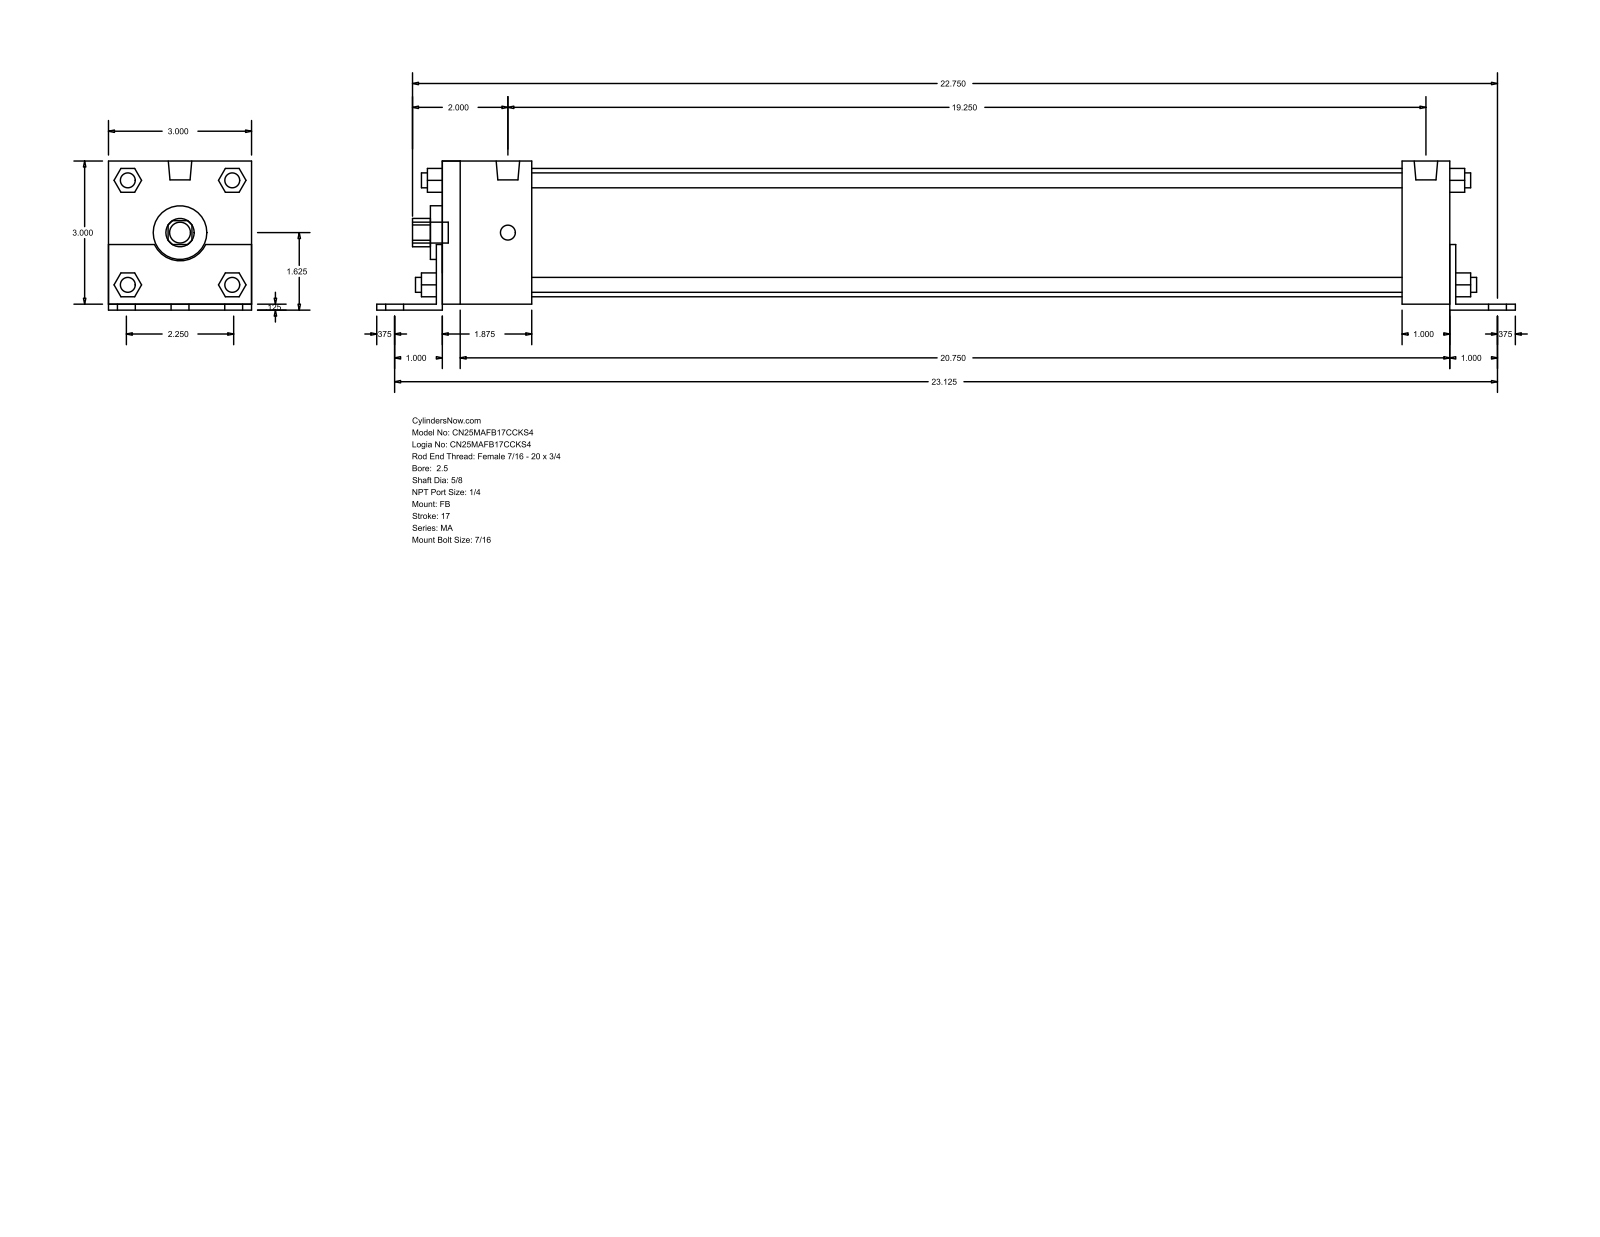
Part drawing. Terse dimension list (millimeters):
name: MA_FB__0250_0.625
written by: GSSL Pune (CONFIG_CONTROL_DESIGN)
unit: mm
bodies: 0 solids, 140 faces (105 planar, 35 cylindrical, 0 other)
size: 606.42 × 79.38 × 76.2
holes: 1× ⌀15.88, 1× ⌀28.57, 1× ⌀68.33
bosses: 8× ⌀7.94, 7× ⌀11.11, 2× ⌀12.49
rounds: 1× R7.54, 1× R15.05
face distances: 76.2, 3.17, 79.37, 536.57, 542.92, 3.18, 539.74, 47.62, 25.4, 539.75
